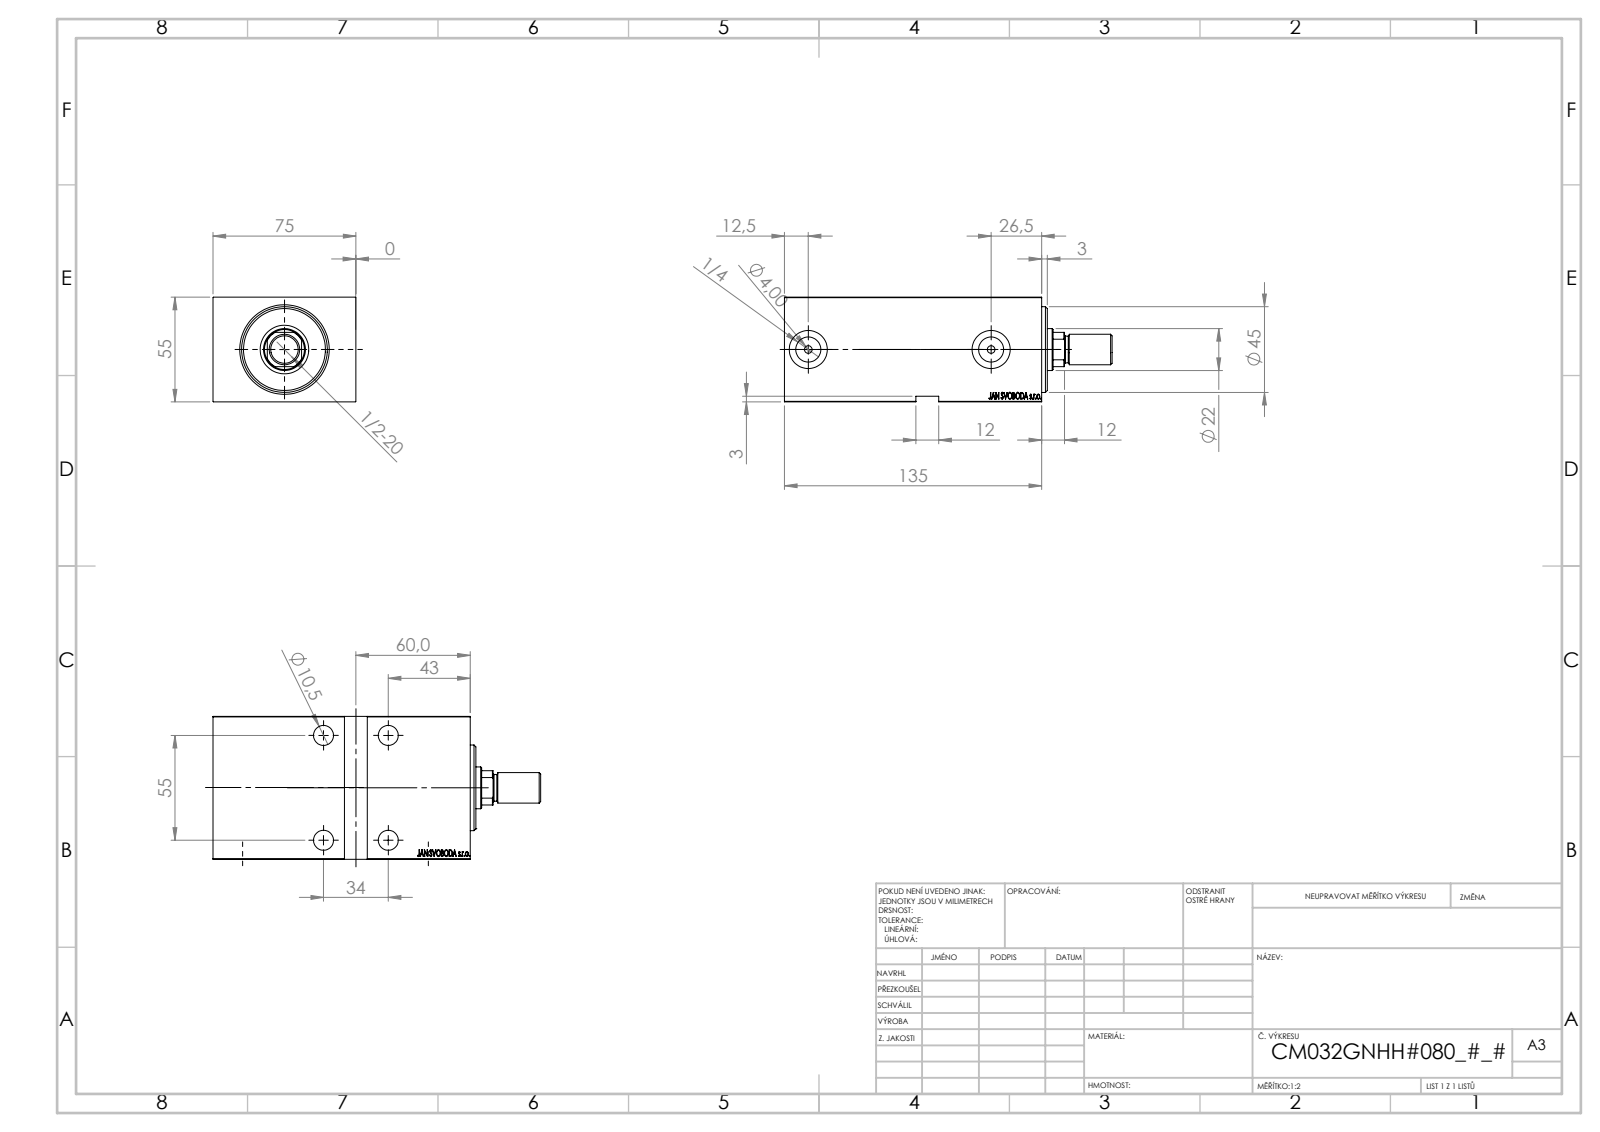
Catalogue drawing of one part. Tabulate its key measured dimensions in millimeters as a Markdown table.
| quantity | value |
| --- | --- |
| part name | V450CM_MALE_METRIC; V450CM_VC_G; V450CM_G_Body; V450CM_G_VCP (+1 more) |
| STEP written by | SolidWorks 2019 (CONFIG_CONTROL_DESIGN) |
| units | millimeters |
| bodies | 6 solids, 907 faces (443 planar, 60 cylindrical, 404 other) |
| overall size | 172 × 75 × 55 |
| volume | 500 001 mm³ |
| surface area | 86 579 mm² |
| round holes (diameter × count) | 10.5 × 5, 16.5 × 4, 4 × 2, 13.16 × 2, 20 × 2, 22 × 1, 25.5 × 1, 32 × 1, 34 × 1, 45 × 1 |
| round bosses / shafts (diameter × count) | 18 × 2, 27 × 1, 16 × 1, 14 × 1 |
| partial cylindrical surfaces (radius × count) | 10.5 × 1 |
| main face-to-face distances | 55, 75, 135, 5, 3, 130, 125, 10, 120, 138 |
| hole center spacings | 34, 55, 64.66, 96 |
